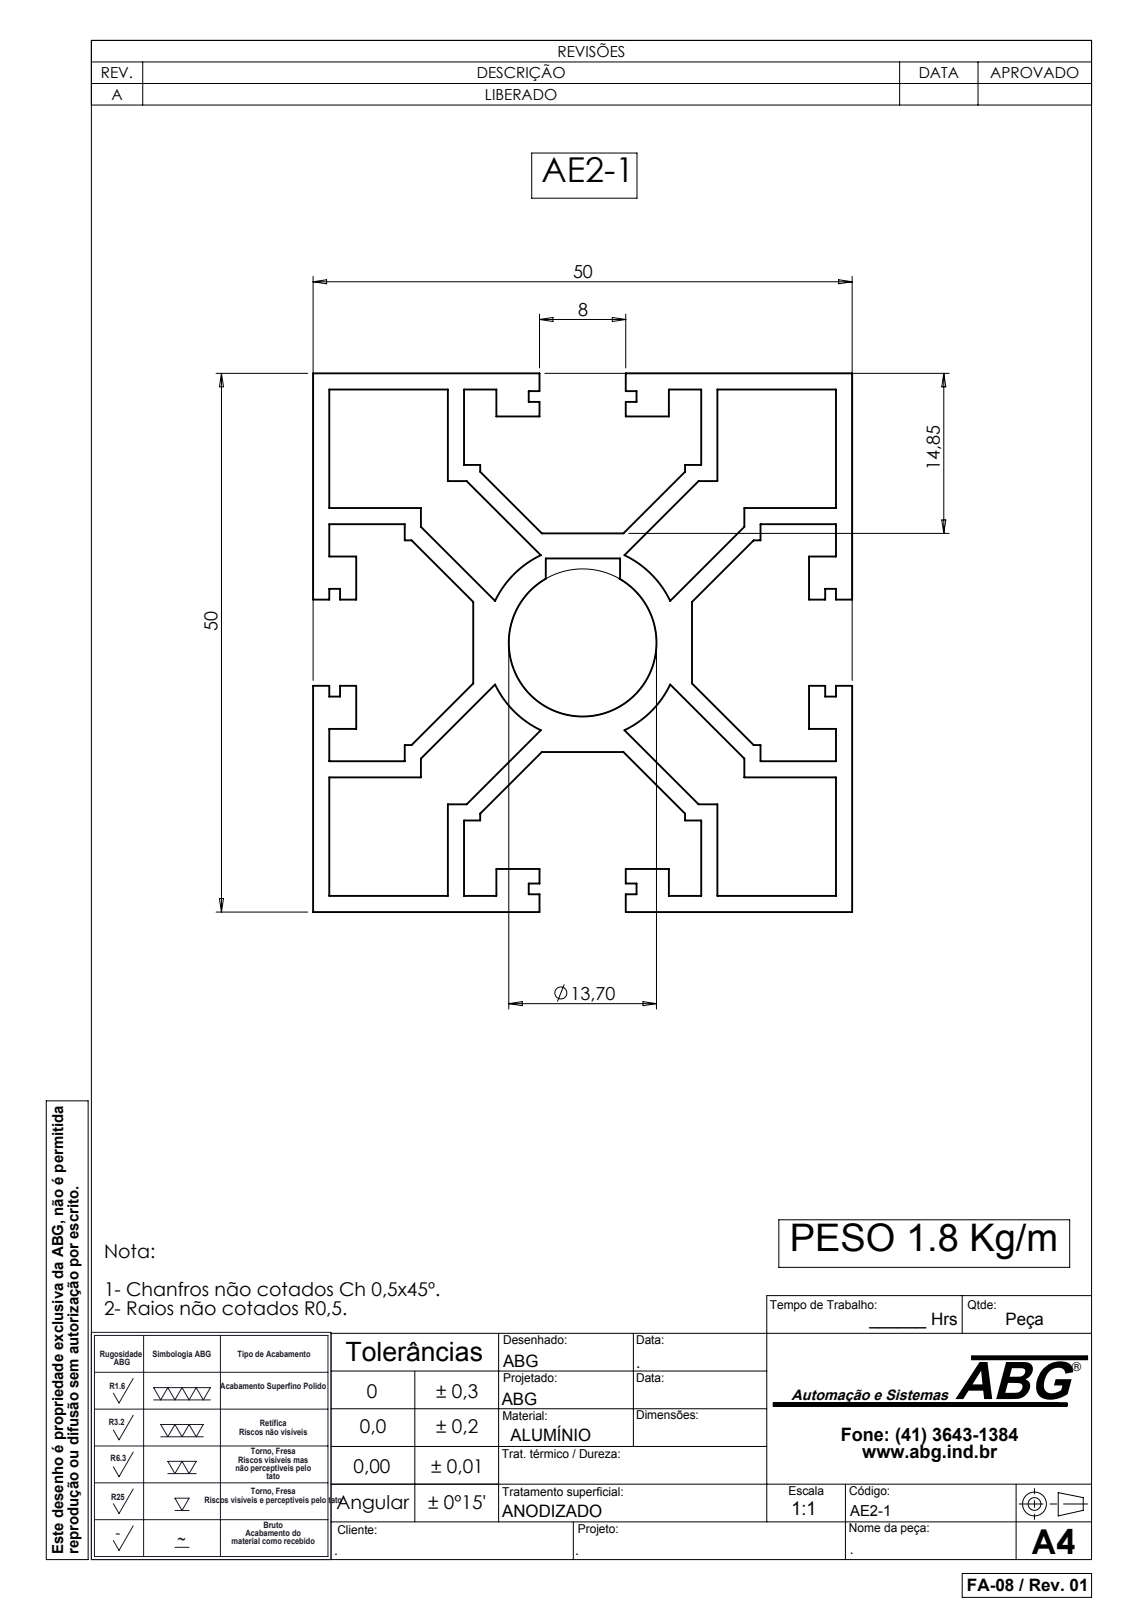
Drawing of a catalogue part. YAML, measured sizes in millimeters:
part_name: "AE2-1"
step_written_by: "SolidWorks 2007 (CONFIG_CONTROL_DESIGN)"
units: millimeters
bodies: {solids: 1, faces: 153, planar: 146, cylindrical: 7, other: 0}
overall_size: [6000, 50, 50]
volume: 4077000
surface_area: 4675000
round_holes:
  - {diameter: 13.7, count: 1}
partial_cylinders:
  - {radius: 9, count: 1}
face_to_face_distances: [1.5, 36, 12.5, 48.5, 8.5, 50, 11, 37.5, 4, 7.5]
